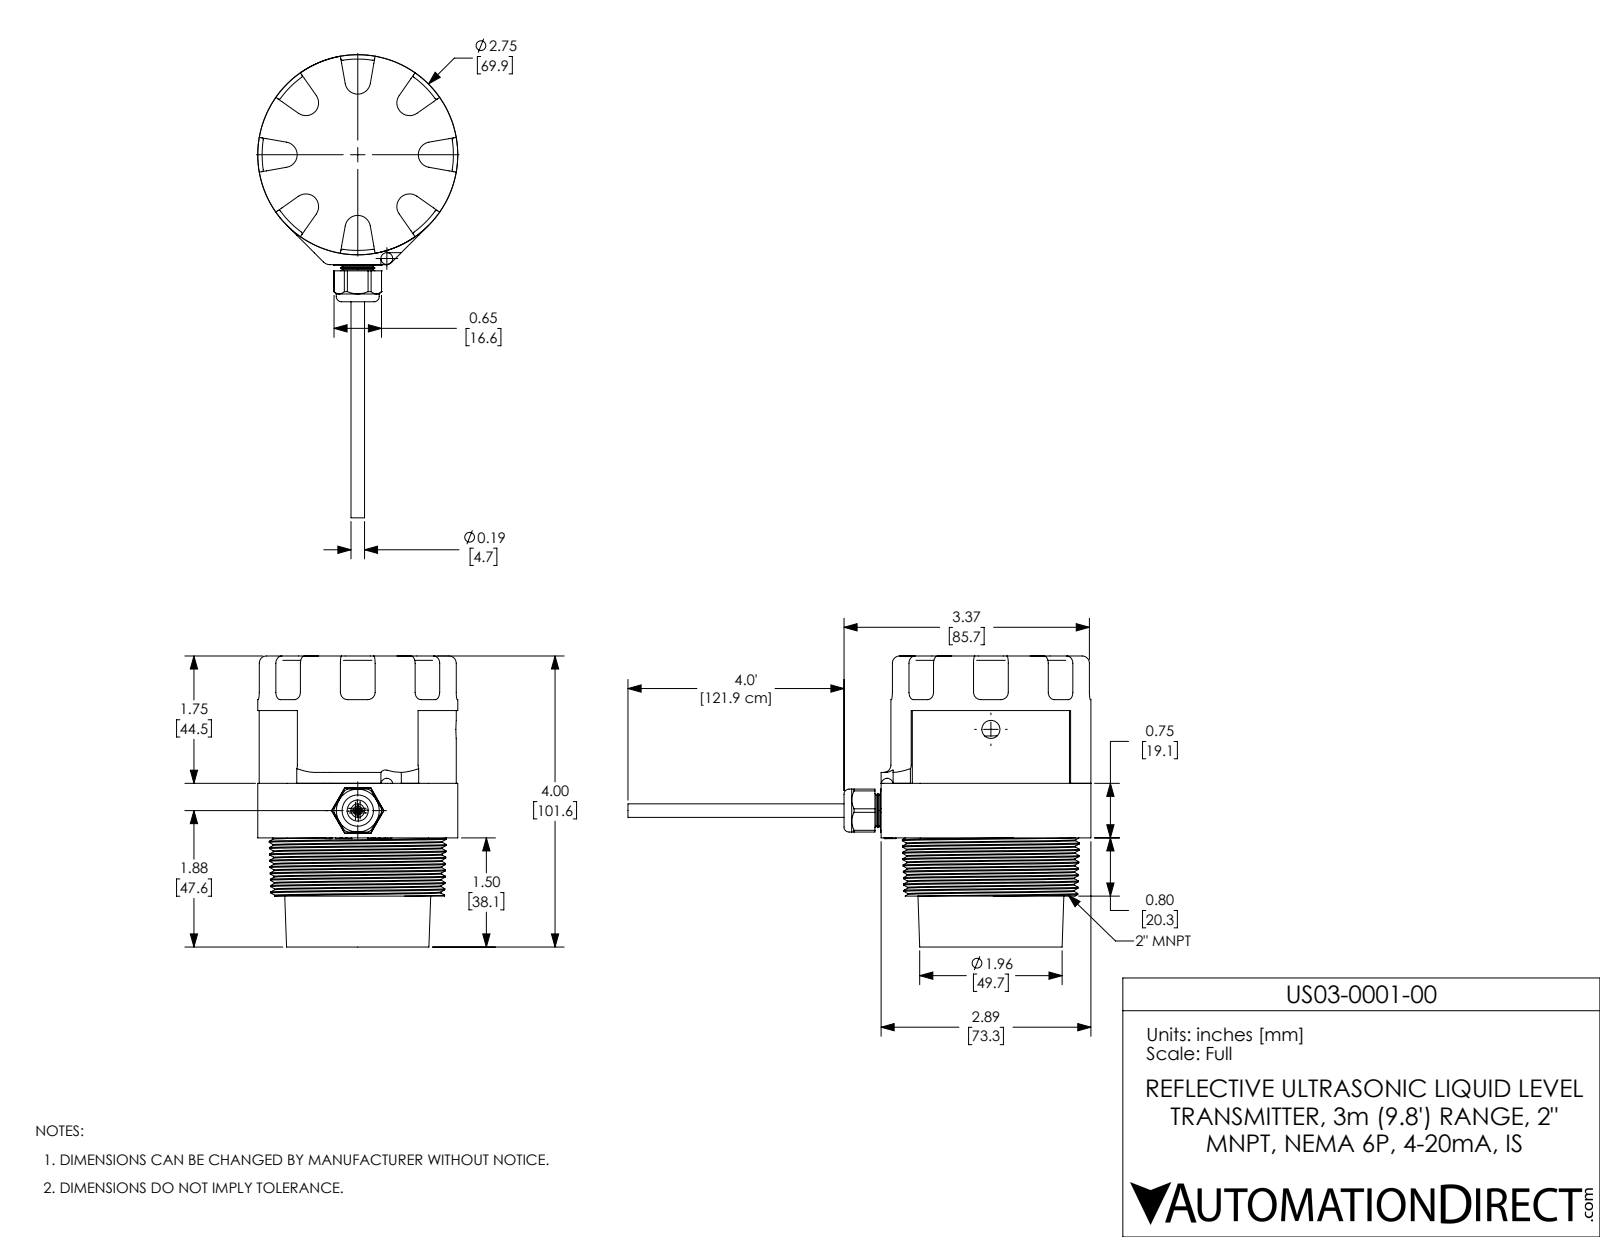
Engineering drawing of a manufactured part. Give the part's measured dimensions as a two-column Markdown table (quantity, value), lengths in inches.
| quantity | value |
| --- | --- |
| part name | US03-0001-40 |
| STEP written by | SolidWorks 2017 (AUTOMOTIVE_DESIGN) |
| units | inches |
| bodies | 11 solids, 772 faces (253 planar, 167 cylindrical, 352 other) |
| overall size | 4.969 × 4.969 × 4 |
| volume | 8.666 in³ |
| surface area | 126.9 in² |
| round holes (diameter × count) | 0.086 × 1, 0.126 × 1, 0.25 × 1, 0.29 × 1, 0.431 × 1, 1.9 × 1, 2.244 × 1, 2.347 × 1, 2.588 × 1 |
| round bosses / shafts (diameter × count) | 0.045 × 4, 2.75 × 1, 2.362 × 1, 2.231 × 1, 1.725 × 1, 1.665 × 1, 0.59 × 1, 0.186 × 1 |
| partial cylindrical surfaces (radius × count) | 0.025 × 32, 0.1 × 16, 0.175 × 8, 0.125 × 2, 0.082 × 1, 0.327 × 1, 0.902 × 1, 1.315 × 1 |
| main face-to-face distances | 0.25, 1.75, 1.5, 0.75, 2.5, 2.25, 0.035, 0.035, 1.25, 0.5 |
| hole center spacings | 1.481 |
